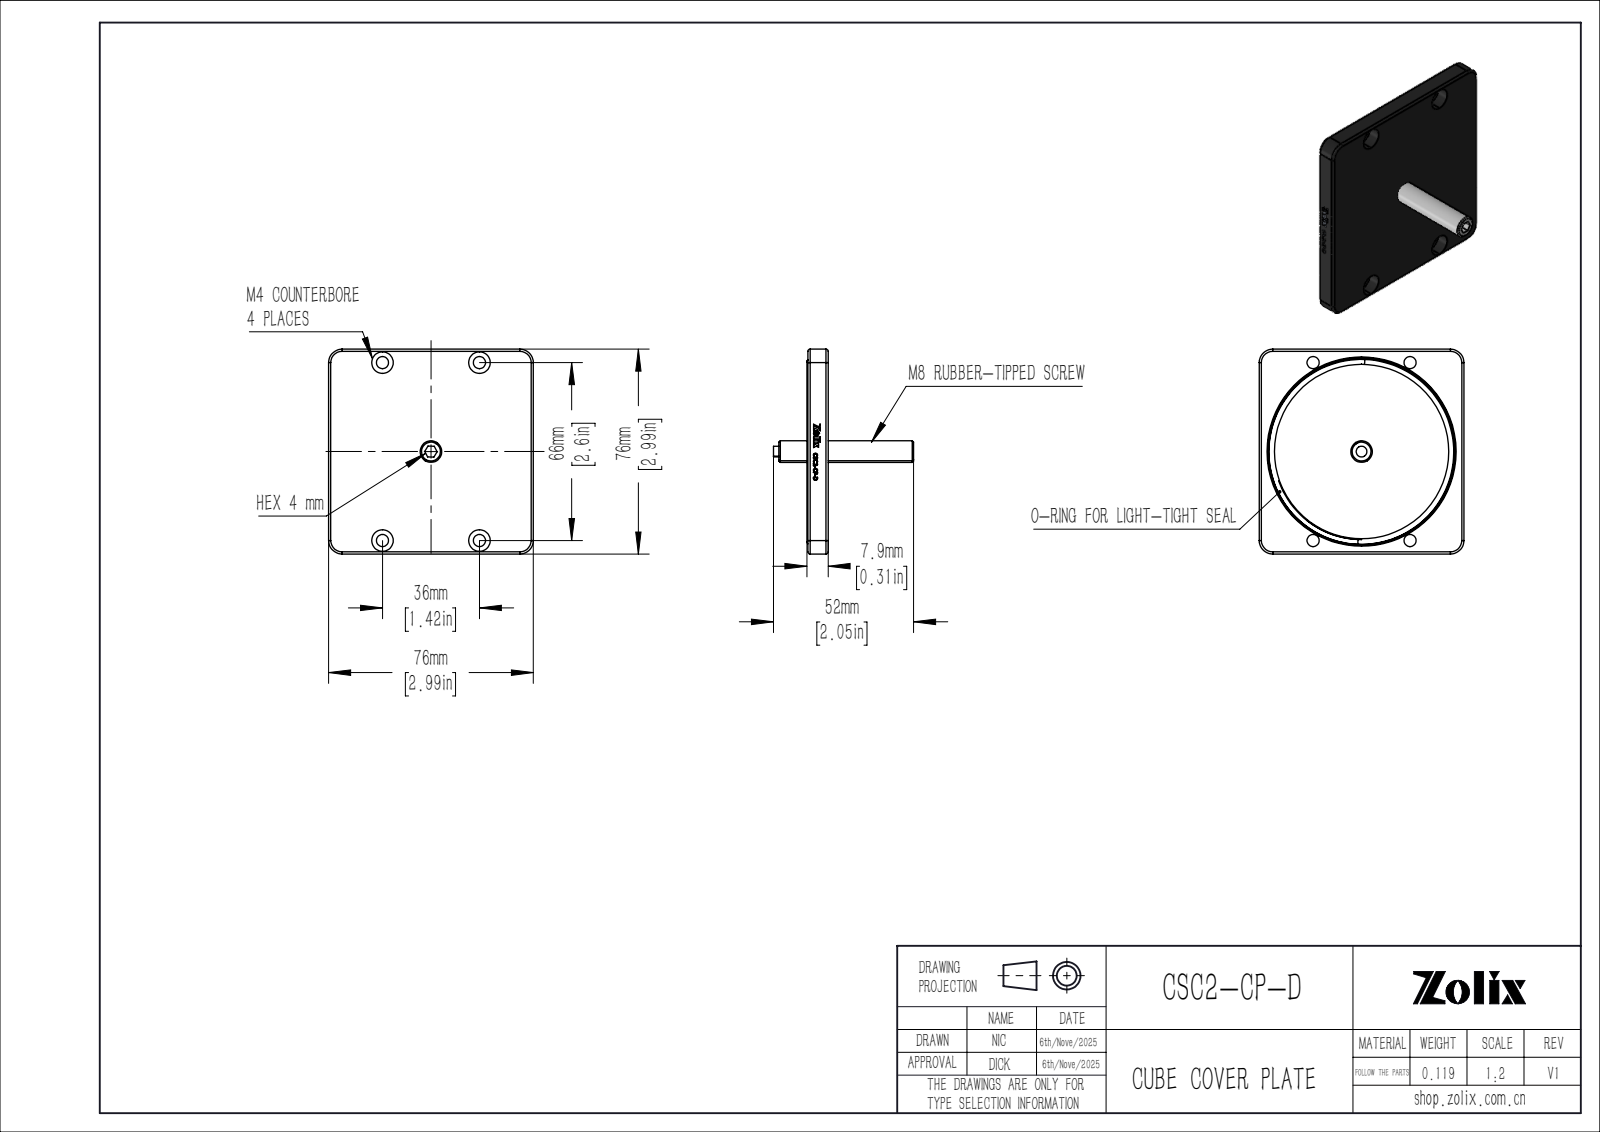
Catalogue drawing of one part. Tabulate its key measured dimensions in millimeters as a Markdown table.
| quantity | value |
| --- | --- |
| part name | CSC2-CP-D |
| STEP written by | SolidWorks 2020 (CONFIG_CONTROL_DESIGN) |
| units | millimeters |
| bodies | 3 solids, 365 faces (227 planar, 38 cylindrical, 100 other) |
| overall size | 76 × 76 × 52 |
| volume | 44 082 mm³ |
| surface area | 17 185 mm² |
| round holes (diameter × count) | 4.5 × 4, 8 × 4, 6.8 × 1, 69.6 × 1 |
| round bosses / shafts (diameter × count) | 65.3 × 1, 8 × 1, 4 × 1 |
| partial cylindrical surfaces (radius × count) | 0.8 × 8, 5 × 4 |
| main face-to-face distances | 7.5, 76, 1.4, 6.1, 2.9, 4.6, 1.5, 10.78, 12.18, 13.68 |
| hole center spacings | 37.59, 36, 66, 75.18 |
